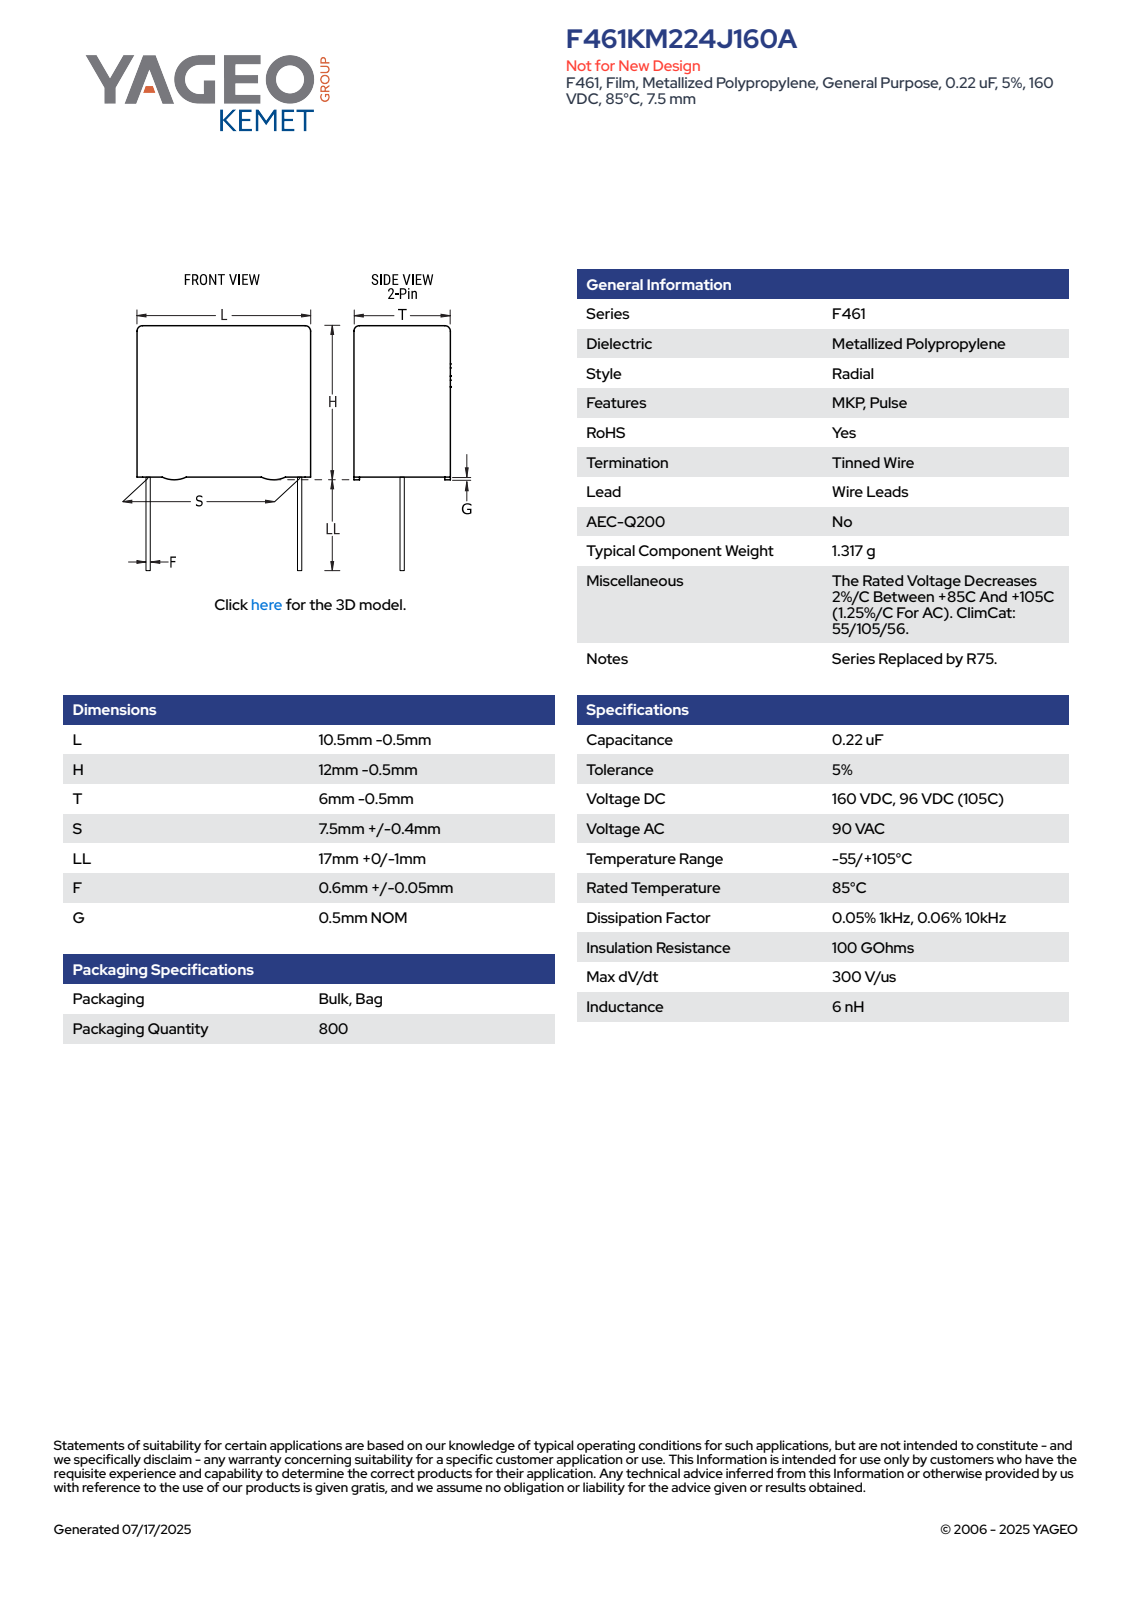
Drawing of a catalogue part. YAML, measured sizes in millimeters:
part_name: "CFR_RBG_10.5X12X6_L10H11.5T5.5S7.5LL17F0.65G0.5"
step_written_by: "SolidWorks 2014 (AUTOMOTIVE_DESIGN)"
units: millimeters
bodies: {solids: 4, faces: 89, planar: 81, cylindrical: 8, other: 0}
overall_size: [28.5, 10, 5.5]
volume: 616
surface_area: 534
round_bosses_or_shafts:
  - {diameter: 0.65, count: 2}
partial_cylinders:
  - {radius: 0.5, count: 4}
face_to_face_distances: [5.5, 10, 11, 5.19, 0.31, 0.5, 11.5, 4.88, 17, 17.5]
